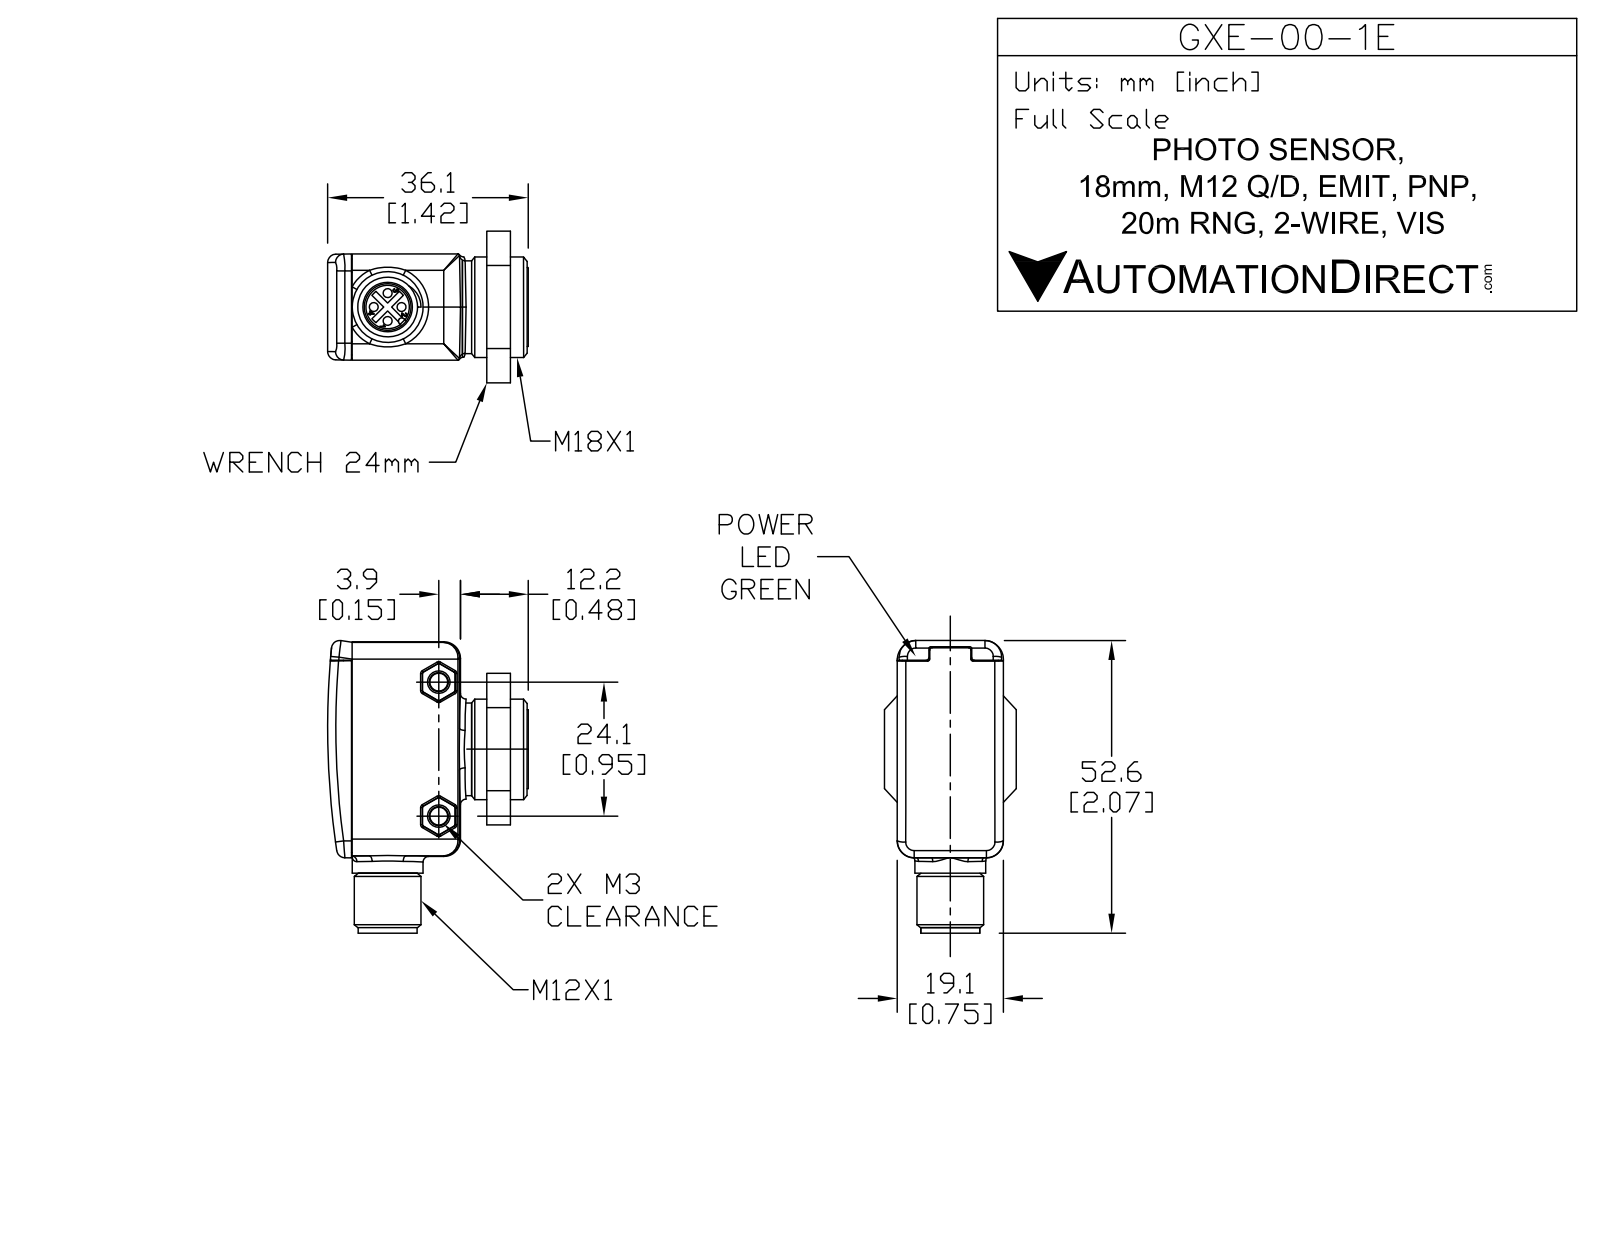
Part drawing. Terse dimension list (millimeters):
name: GXE-00-1E
written by: SolidWorks 2013 (AUTOMOTIVE_DESIGN)
unit: mm
bodies: 1 solid, 107 faces (60 planar, 33 cylindrical, 14 other)
size: 52.66 × 36.1 × 23.85
volume: 21 253 mm³; area: 6 452 mm²
holes: 2× ⌀3.2, 1× ⌀8.36
bosses: 1× ⌀18, 1× ⌀17.5, 1× ⌀14.2, 1× ⌀12.68, 1× ⌀11.55, 1× ⌀10.6
rounds: 8× R1.5, 4× R1, 1× R139.57
face distances: 19.1, 7.2, 2.12, 9.32, 19.2, 5, 2.88, 12.2, 38.8, 5.95
hole spacings: 24.1
